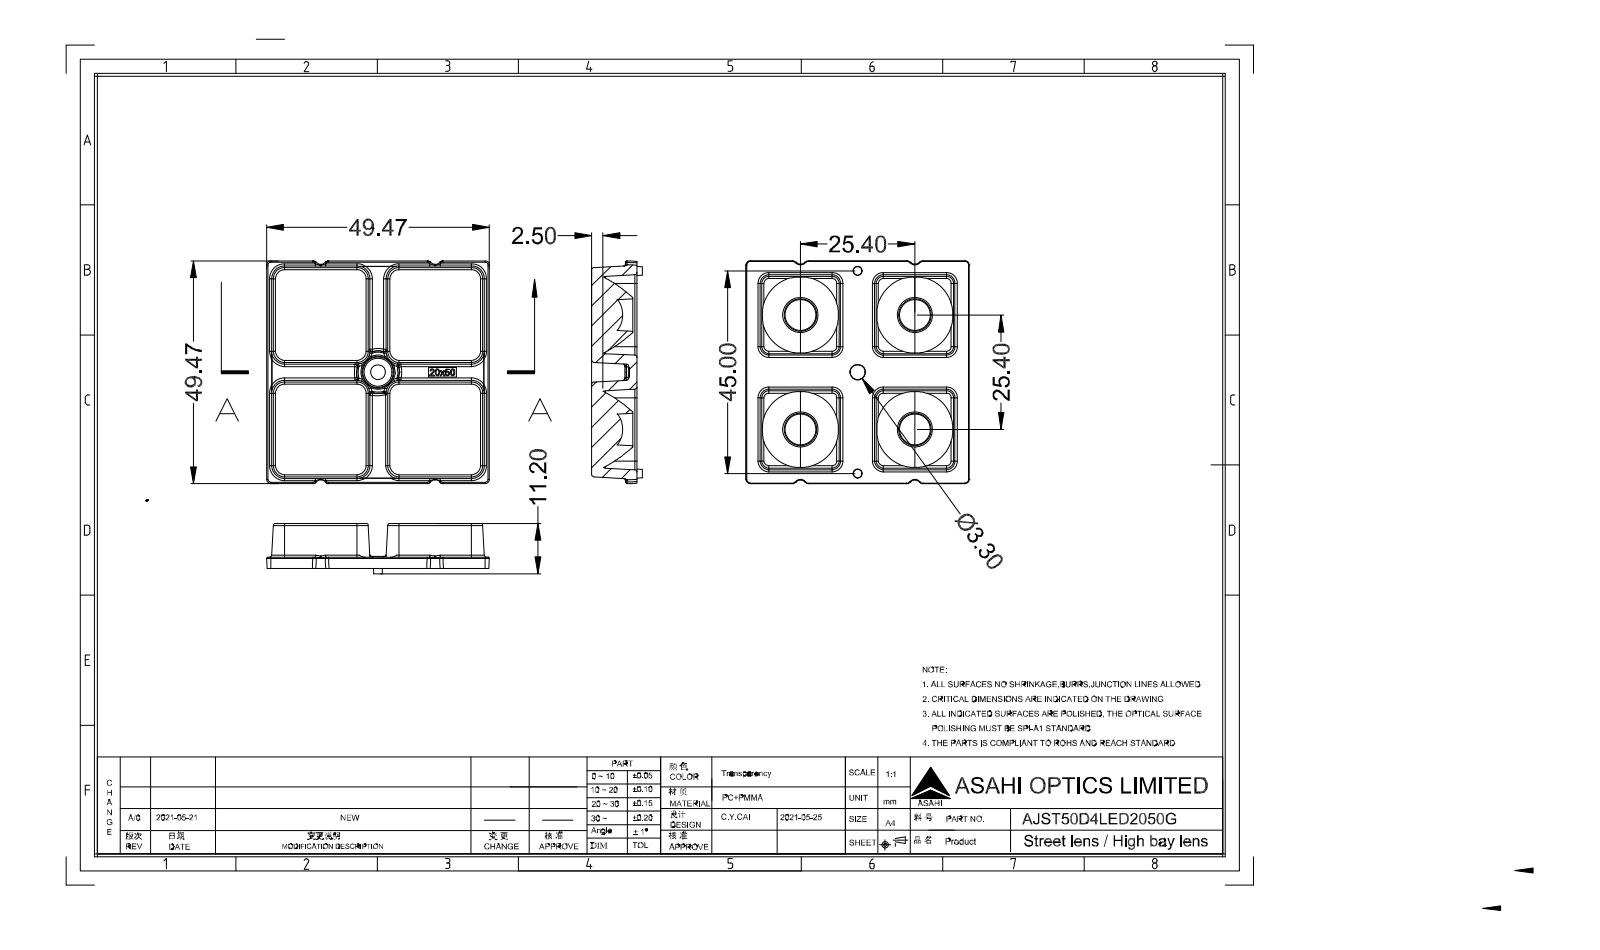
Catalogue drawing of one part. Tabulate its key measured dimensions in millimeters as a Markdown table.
| quantity | value |
| --- | --- |
| part name | AdmiB0685A81pma6 |
| STEP written by | SIEMENS PLM Software NX 10.0 (AUTOMOTIVE_DESIGN) |
| units | millimeters |
| bodies | 2 solids, 471 faces (149 planar, 78 cylindrical, 244 other) |
| overall size | 49.47 × 49.47 × 11.5 |
| volume | 17 193 mm³ |
| surface area | 15 455 mm² |
| round holes (diameter × count) | 2.1 × 2, 3.5 × 1 |
| partial cylindrical surfaces (radius × count) | 0.5 × 32, 0.3 × 4 |
| main face-to-face distances | 1.5, 11.5, 10, 2.1, 25.37, 25.38, 20.84, 22.94, 27.47, 23.28 |
| hole center spacings | 22.5, 45 |
